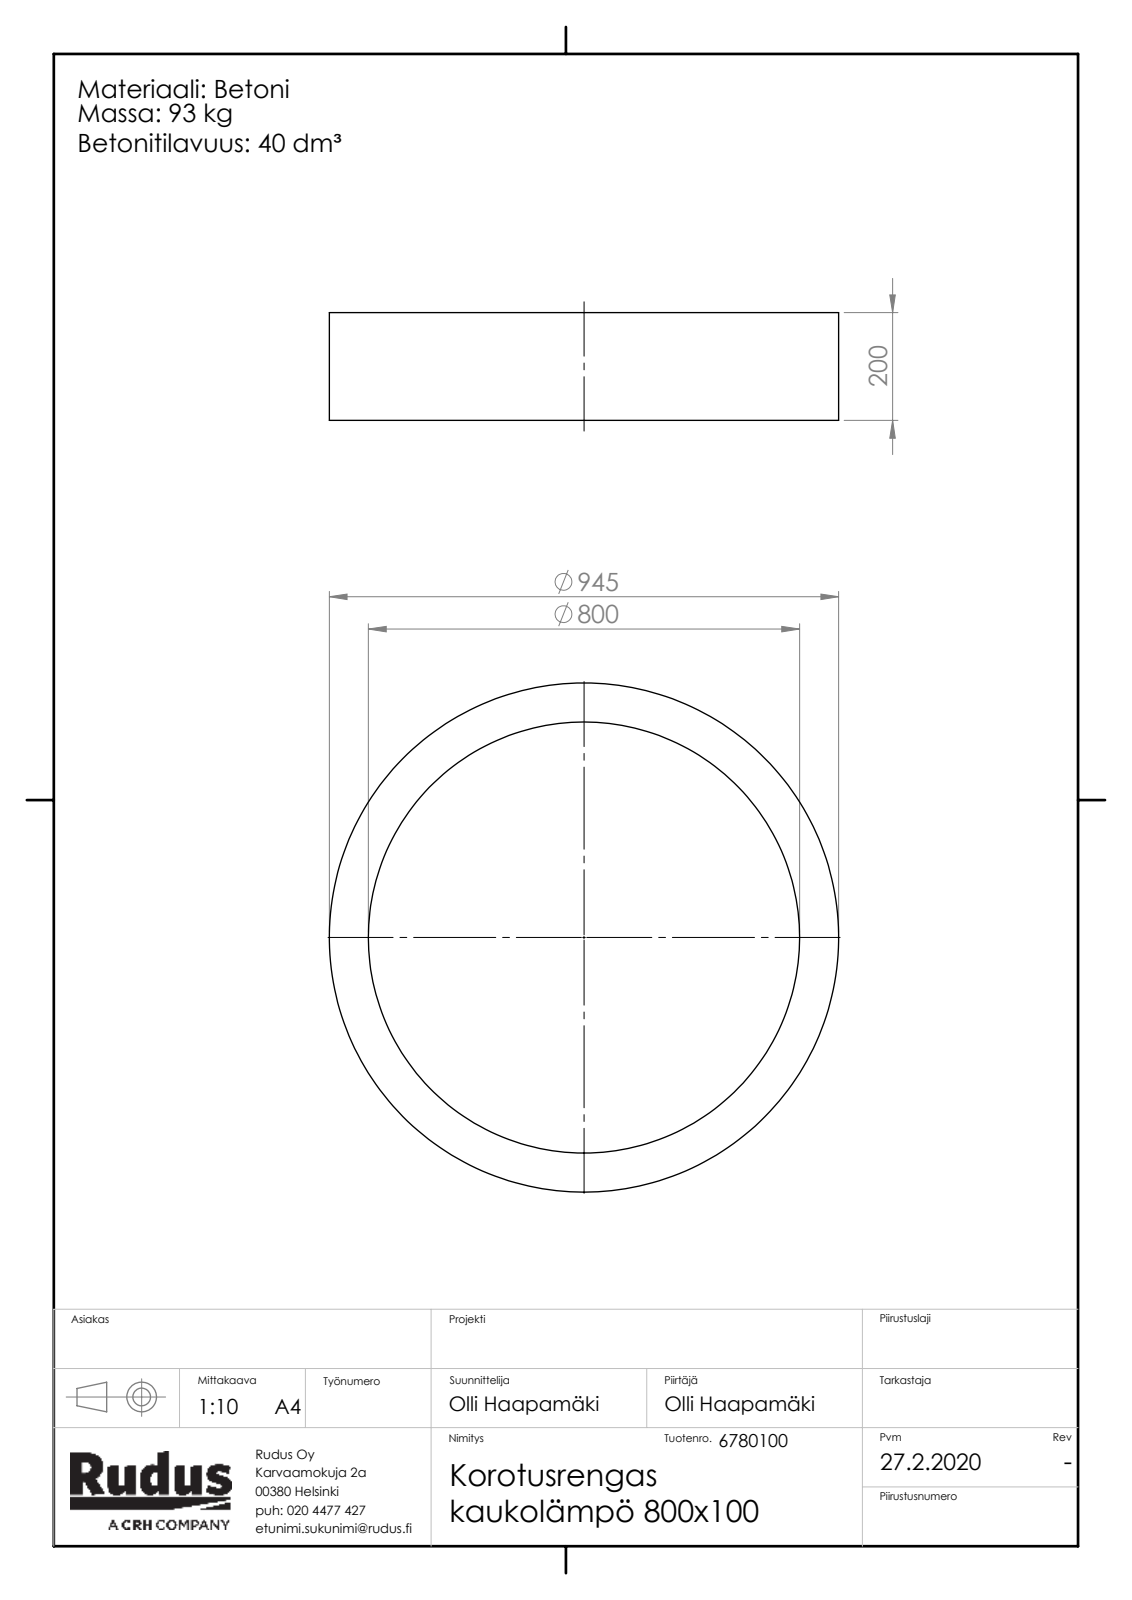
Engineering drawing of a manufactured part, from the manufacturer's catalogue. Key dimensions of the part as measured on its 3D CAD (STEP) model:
Part name (STEP PRODUCT): kaivo-osa-korotusrengas_Kaukolmp; Rudus 6780200 Korotusrengas kaukolämpö 800x200
STEP written by: SolidWorks 2019 (CONFIG_CONTROL_DESIGN)
Units: millimetres
Bodies: 1 solid, 6 faces (2 planar, 4 cylindrical, 0 other)
Overall size (bounding box): 945 × 945 × 200
Volume: 39 750 000 mm³ · Surface area: 1 494 000 mm²
Round holes (diameter × count): ⌀800 ×1
Round bosses / shafts (diameter × count): ⌀945 ×1
Main face-to-face distances: 200
